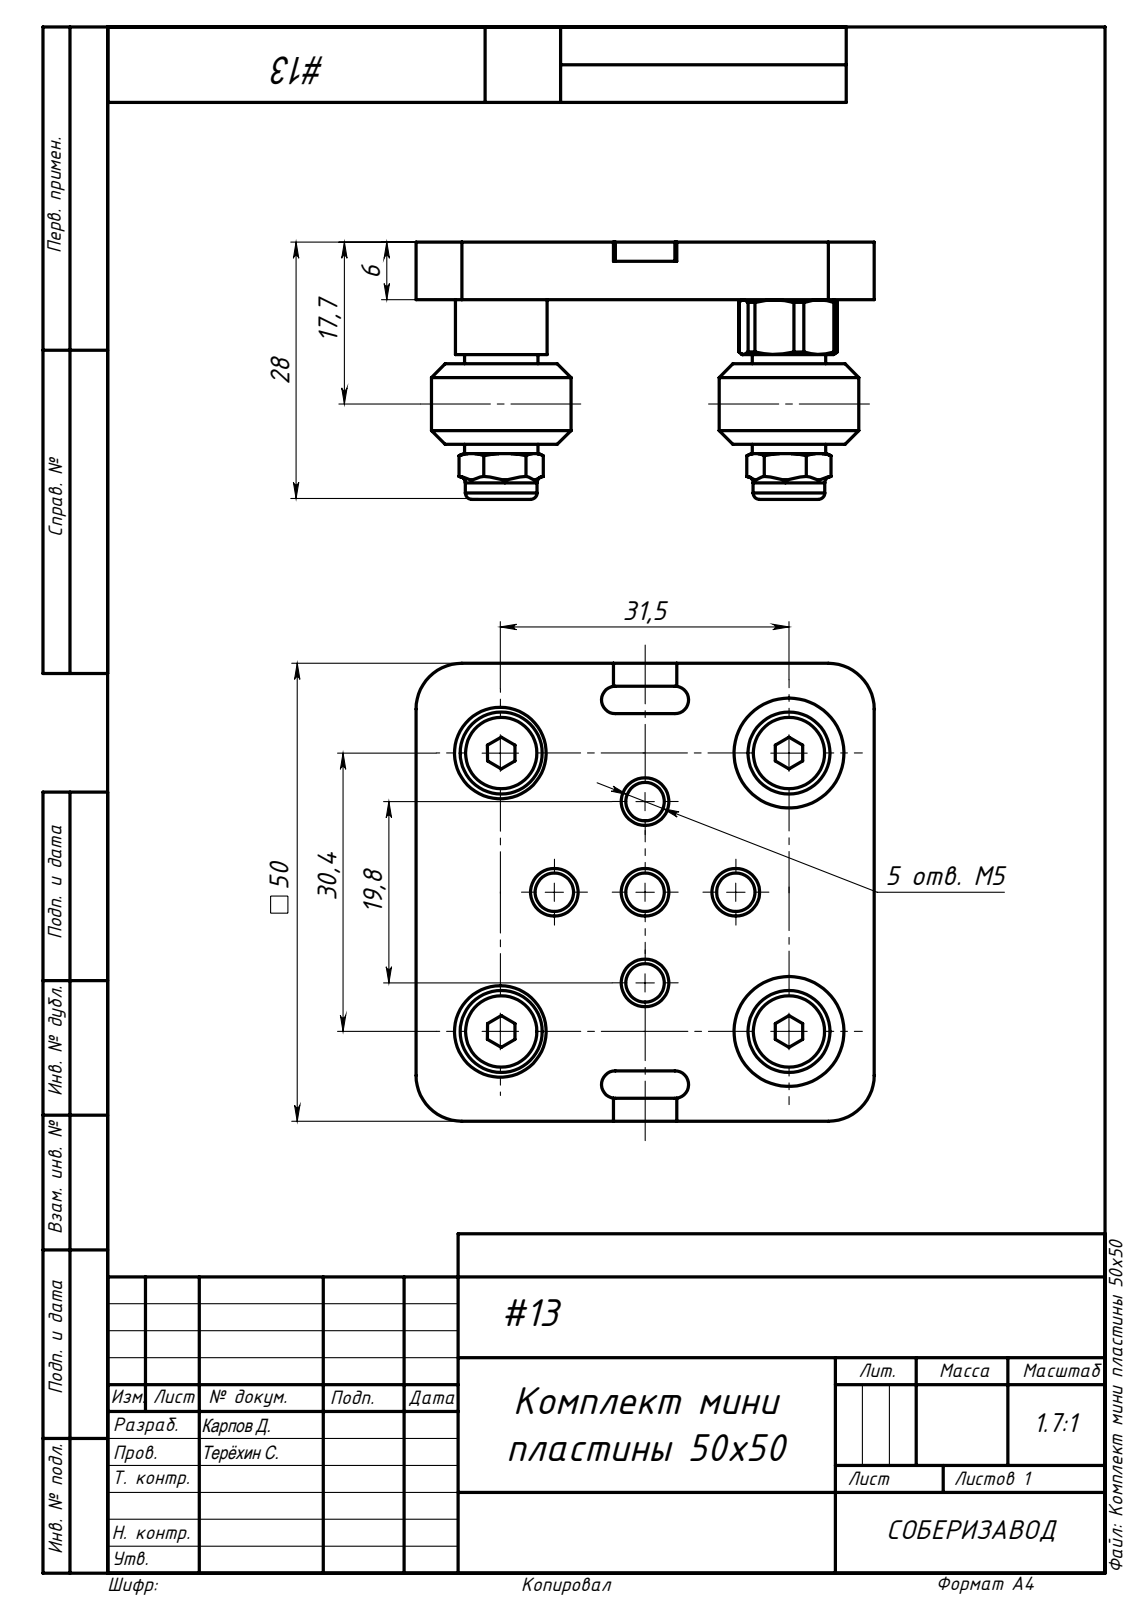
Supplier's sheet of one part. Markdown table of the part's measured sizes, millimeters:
| quantity | value |
| --- | --- |
| part name | A183 Подшипник для мини роликов, O 5 O 10, MR105zz_00; A137 Высокоточная прокладка O 5,3 O 8; A201 Дистанционная втулка 5х6 мм_00; A229 Самоконтрящаяся гайка M5_00 (+4 more) |
| STEP written by | SolidWorks 2020 (AUTOMOTIVE_DESIGN) |
| units | millimeters |
| bodies | 69 solids, 1432 faces (286 planar, 414 cylindrical, 732 other) |
| overall size | 50 × 50 × 28.1 |
| volume | 22 744 mm³ |
| surface area | 21 643 mm² |
| round holes (diameter × count) | 5 × 6, 4.2 × 5, 4.13 × 4, 5.15 × 4, 5.3 × 4, 6.09 × 4, 7.8 × 4, 8.4 × 4, 8.65 × 4, 10 × 4, 7 × 2, 12 × 2 |
| round bosses / shafts (diameter × count) | 15.23 × 4, 8.95 × 4, 8.64 × 4, 8 × 4, 7.83 × 4, 6.27 × 4, 6 × 4, 10 × 2 |
| partial cylindrical surfaces (radius × count) | 0.2 × 28, 1.5 × 4, 5 × 4 |
| main face-to-face distances | 6.3, 1, 9.8, 4.8, 15.8, 10.8, 4.9, 50, 3, 5 |
| hole center spacings | 30.4, 9.9, 14, 16.27, 16.57, 21.85, 29.61, 29.77 |
